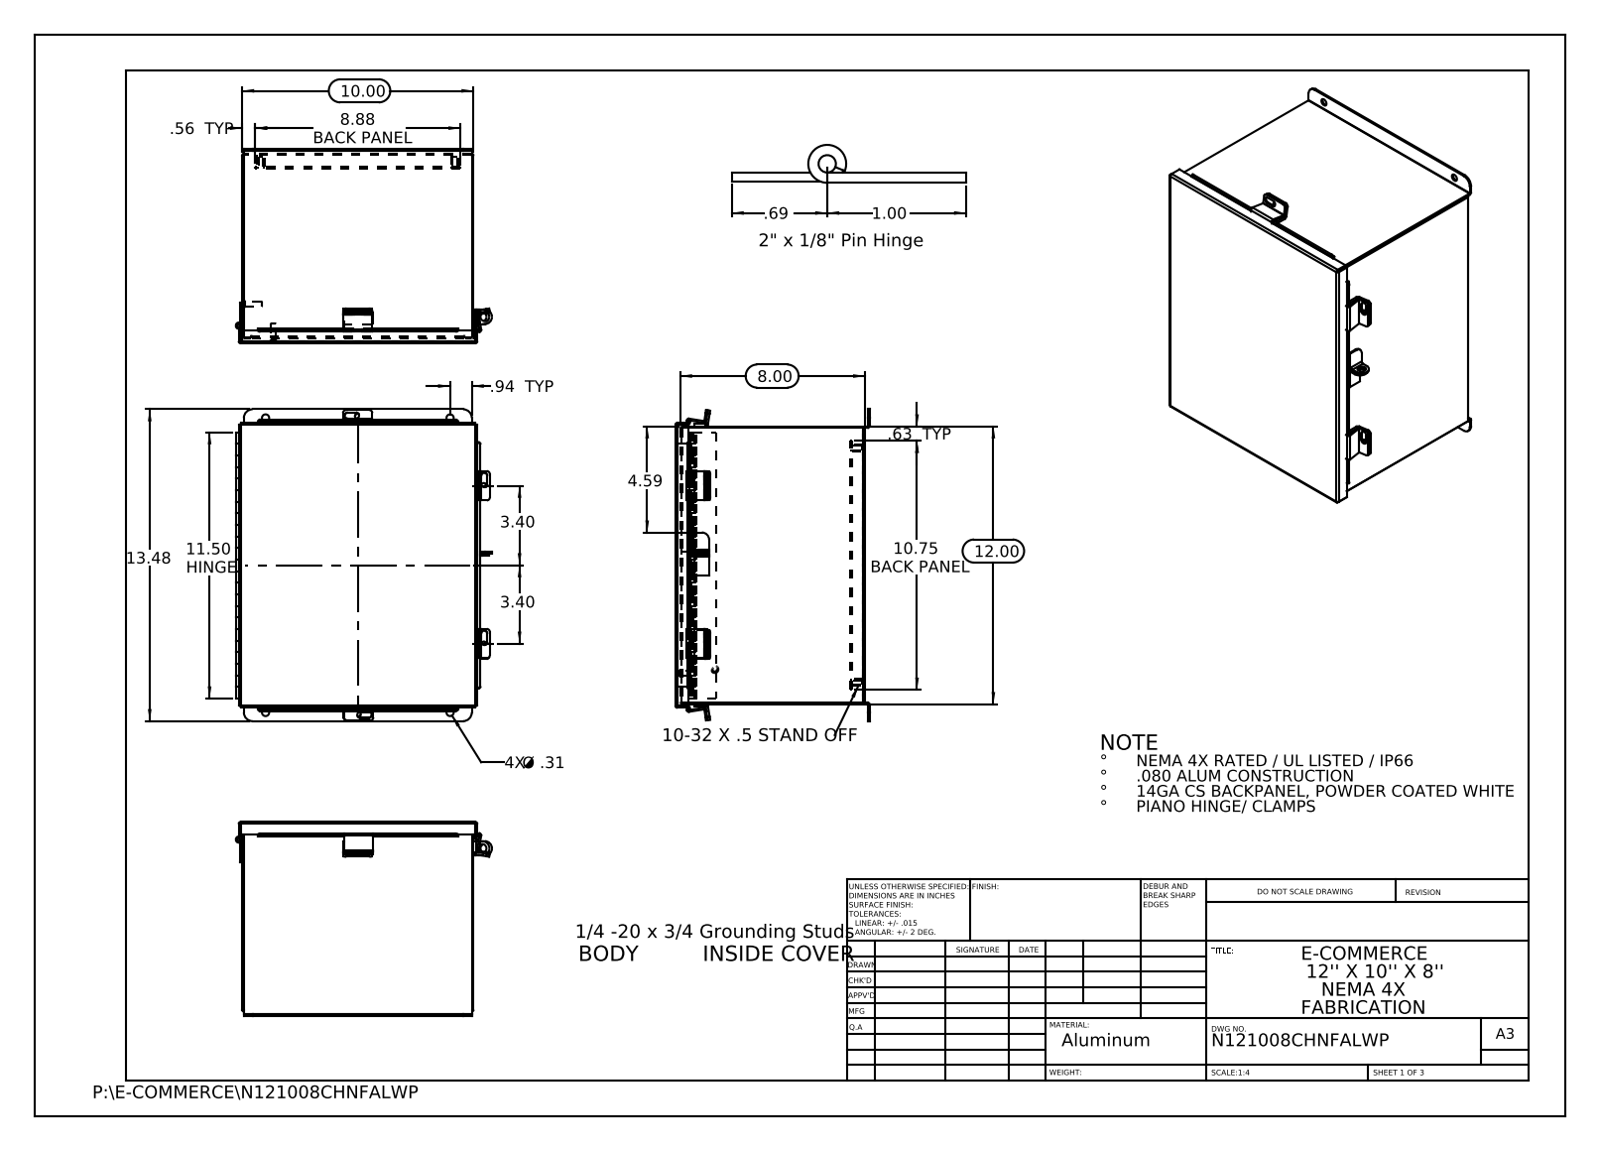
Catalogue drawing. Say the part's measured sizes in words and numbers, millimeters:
The part is named "N121008CHNFALWP Hinge Cover Side JIC; N121008CHNFALWP JIC Top; HW-CLH-JH-20154; HW-CLH-JH-20104 (+8 more)". Its 3-D file was written by "SolidWorks 2013 (CONFIG_CONTROL_DESIGN)". It is 23 solids with 702 faces: 435 planar, 247 cylindrical and 20 other. Overall it measures 342.3 by 281.2 by 213.1 millimeters. Its volume is 955 200 cubic millimeters and its surface area 1 026 000 square millimeters. Round holes: 8 of diameter 6.4, 4 of diameter 4.7, 4 of diameter 7.9, 1 of diameter 3.2, 1 of diameter 3.2, 1 of diameter 9.5, 1 of diameter 9.5. Round bosses or shafts: 4 of diameter 8, 2 of diameter 8, 2 of diameter 6, 1 of diameter 6.9, 1 of diameter 6.4. Partial cylindrical surfaces (rounded edges, fillets, slot ends): 15 of radius 3.2, 13 of radius 0.3, 12 of radius 0.2, 12 of radius 2.2, 8 of radius 3.4, 6 of radius 2.1, 6 of radius 2.5, 4 of radius 9.5. The main face-to-face distances are 1.9, 206.5, 252.1, 302.9, 204.5, 208.4, 1.9, 14.6, 12.7, 191.8. The hole center spacings are 33.4, 210.3, 290.3, 356.9, 202.6, 212.7, 257.2, 323.2.
